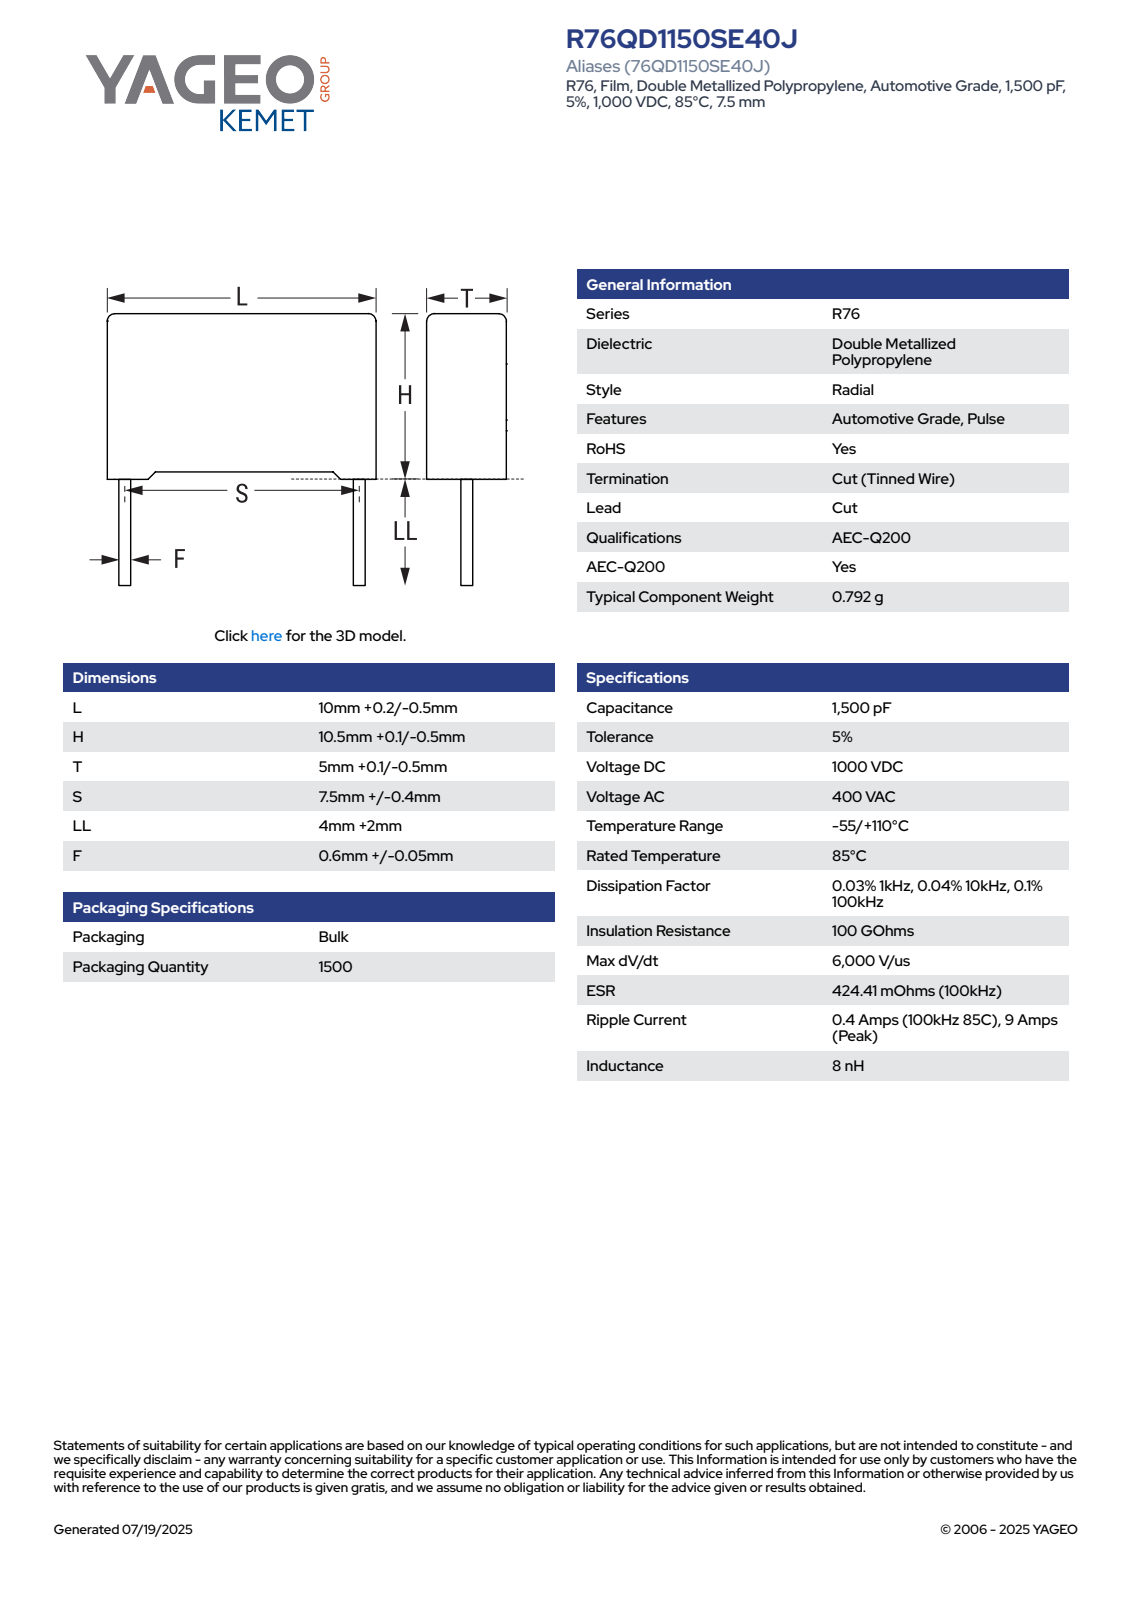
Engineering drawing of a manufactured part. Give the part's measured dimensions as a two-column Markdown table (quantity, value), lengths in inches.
| quantity | value |
| --- | --- |
| part name | CFR_RB2_10X10.5X5_L10.2H10.6T5.1S7.5LL6F0.65 |
| STEP written by | SolidWorks 2021 (AUTOMOTIVE_DESIGN) |
| units | inches |
| bodies | 4 solids, 85 faces (77 planar, 8 cylindrical, 0 other) |
| overall size | 0.654 × 0.402 × 0.201 |
| volume | 0.032 in³ |
| surface area | 0.732 in² |
| round bosses / shafts (diameter × count) | 0.026 × 2 |
| partial cylindrical surfaces (radius × count) | 0.02 × 4 |
| main face-to-face distances | 0.201, 0.402, 0.388, 0.013, 0.187, 0.03, 0.417, 0.388, 0.174, 0.375 |
